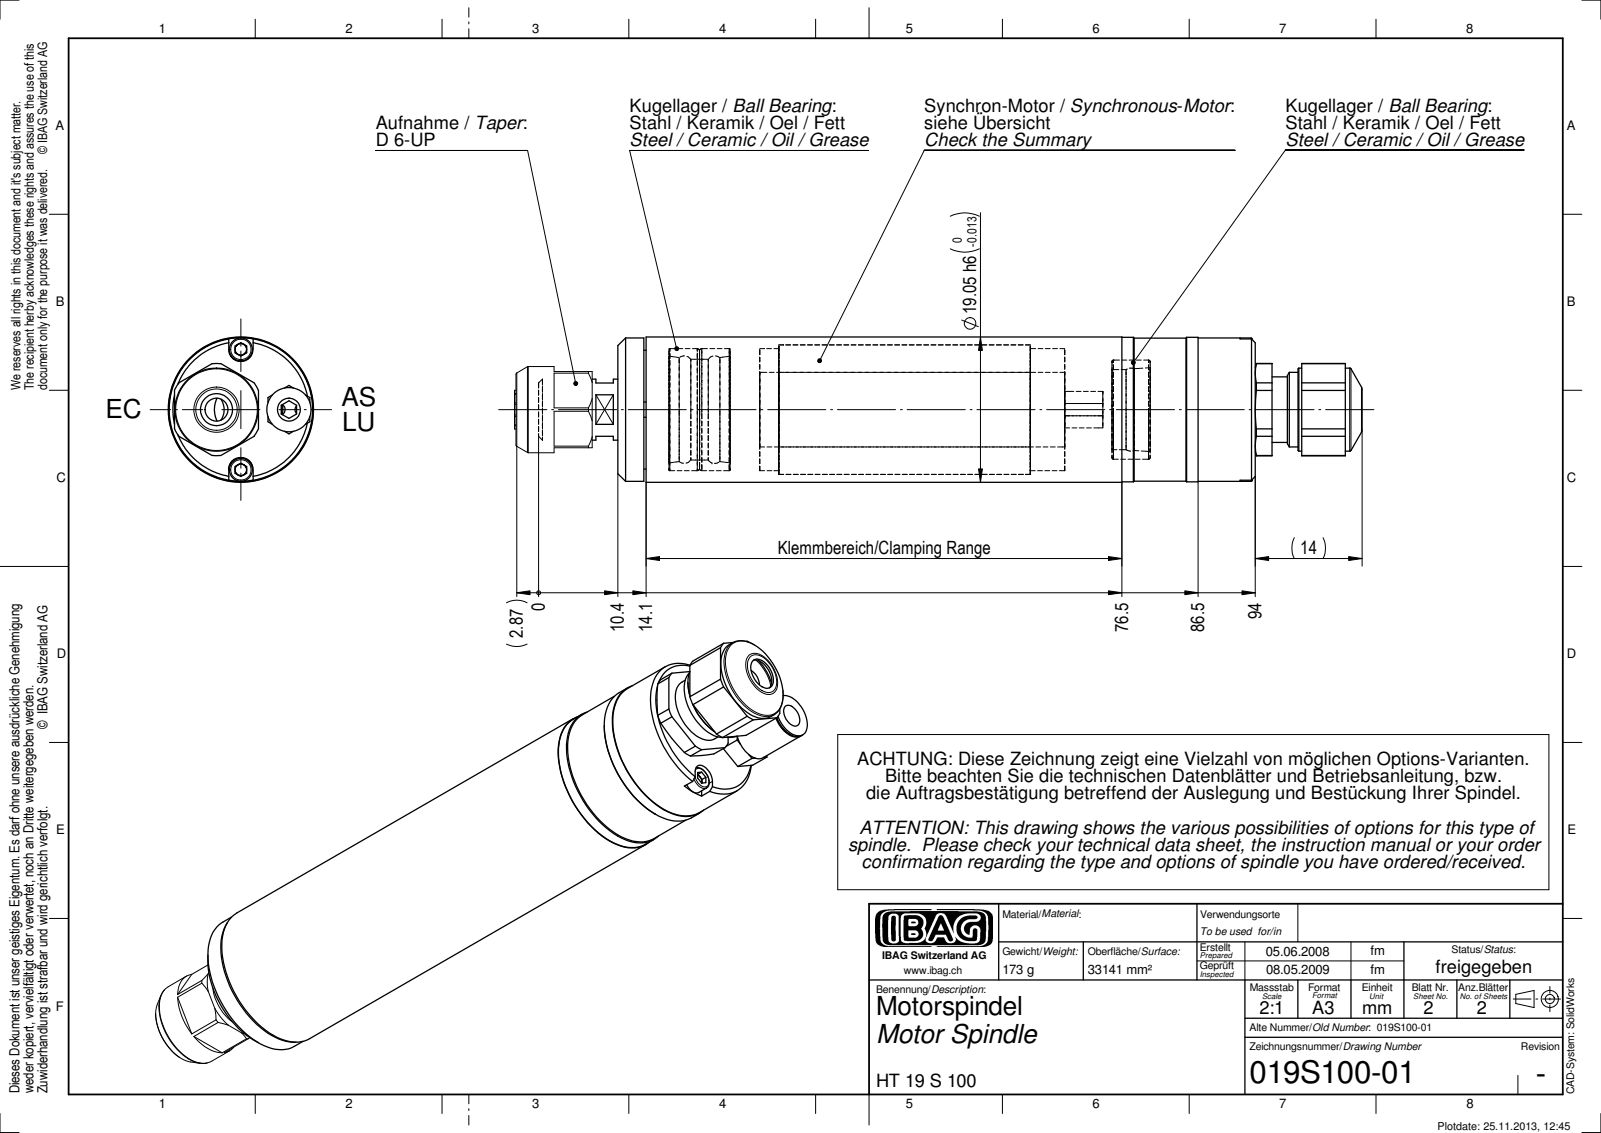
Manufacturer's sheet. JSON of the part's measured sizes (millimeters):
{"part_name": "019S100-01", "step_written_by": "SolidWorks 2010 (CONFIG_CONTROL_DESIGN)", "units": "millimeters", "bodies": {"solids": 0, "faces": 236, "planar": 105, "cylindrical": 87, "other": 44}, "overall_size": [111.17, 19.05, 19.05], "round_holes": [[1.6, 4], [3, 2], [0.5, 1], [4.2, 1], [9.15, 1]], "round_bosses_or_shafts": [[3, 2], [19.05, 1], [18.95, 1], [18.8, 1], [18.75, 1], [11.3, 1], [10.9, 1], [9.79, 1]], "partial_cylinders_radius": [[1.6, 2], [0.75, 1], [6.05, 1]], "face_to_face_distances": [10, 83.6, 7.5, 11, 3.4, 76.1, 2.2, 17.5, 72.7, 80.2], "hole_center_spacings": [5.25, 7.42, 6.15, 8.2, 10.5, 1.05, 2.05, 3.2]}
